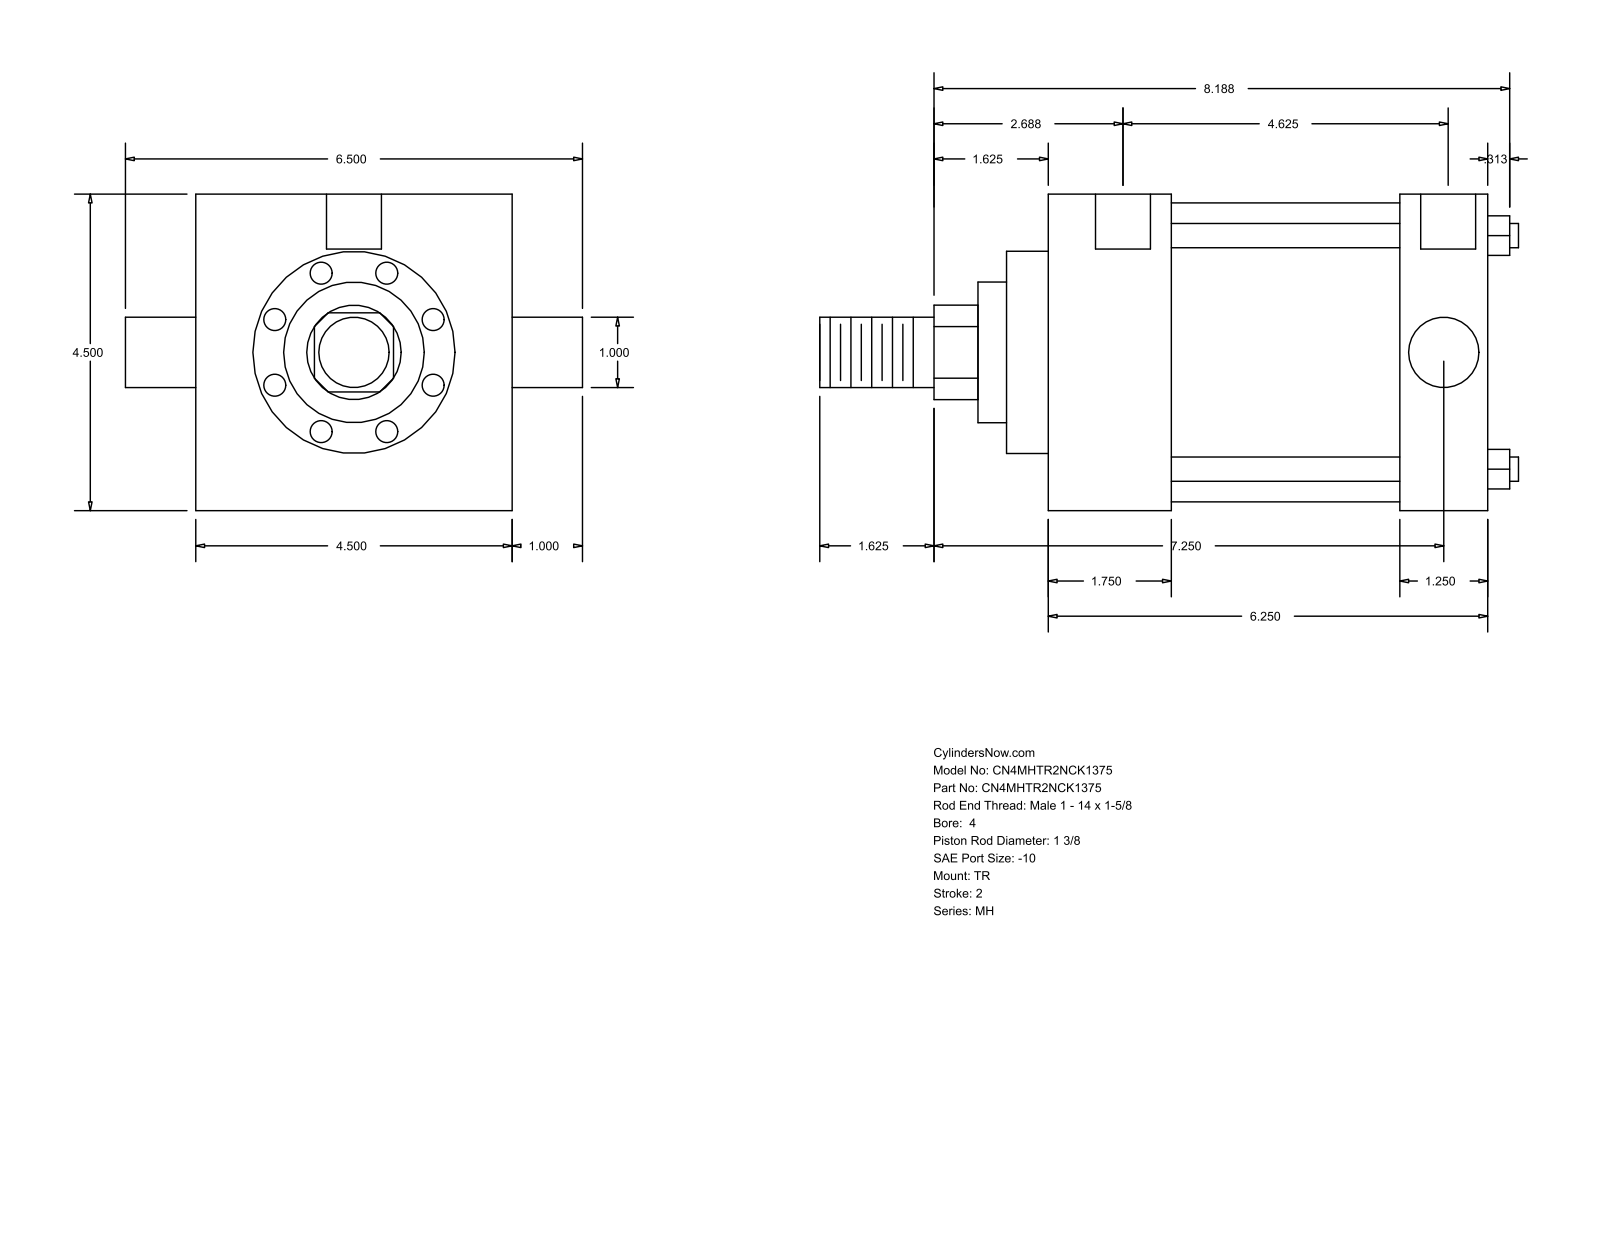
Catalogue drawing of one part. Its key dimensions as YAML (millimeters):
part_name: "MH_TR__0400_1.375"
step_written_by: "GSSL Pune (CONFIG_CONTROL_DESIGN)"
units: millimeters
bodies: {solids: 0, faces: 86, planar: 61, cylindrical: 25, other: 0}
overall_size: [252.41, 165.1, 114.3]
round_holes:
  - {diameter: 8.73, count: 3}
  - {diameter: 19.84, count: 2}
round_bosses_or_shafts:
  - {diameter: 8.76, count: 4}
  - {diameter: 25.4, count: 2}
  - {diameter: 107.95, count: 1}
  - {diameter: 73.03, count: 1}
  - {diameter: 50.8, count: 1}
  - {diameter: 34.92, count: 1}
partial_cylinders:
  - {radius: 17.06, count: 1}
face_to_face_distances: [114.3, 158.76, 44.45, 114.31, 127.01, 82.56, 31.75, 15.08, 59.53, 142.09]
hole_center_spacings: [1.58, 1.59, 117.48, 119.06, 119.07, 120.65]
